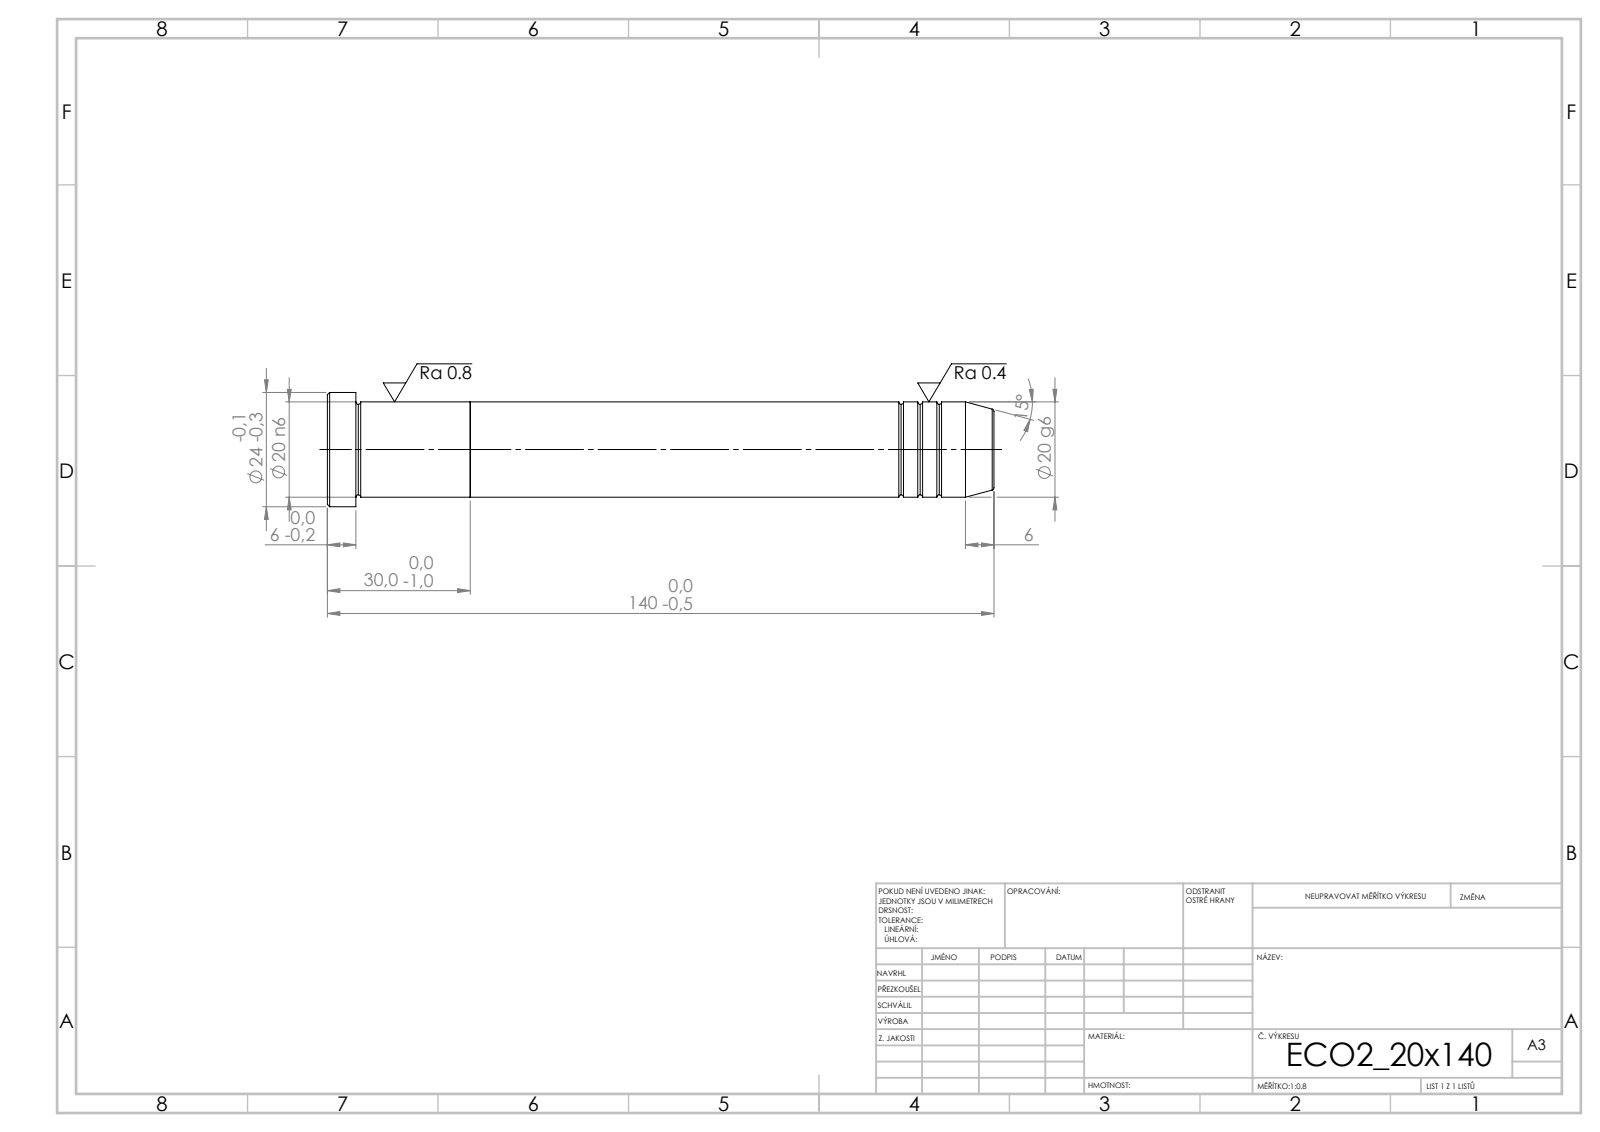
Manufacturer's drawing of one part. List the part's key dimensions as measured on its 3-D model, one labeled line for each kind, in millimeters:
STEP written by: SolidWorks 2019 (CONFIG_CONTROL_DESIGN)
Units: millimetres
Bodies: 2 solids, 39 faces (5 planar, 12 cylindrical, 22 other)
Overall size (bounding box): 140 × 24 × 24
Volume: 44 418 mm³ · Surface area: 10 396 mm²
Round bosses / shafts (diameter × count): ⌀24 ×1, ⌀20 ×1
Main face-to-face distances: 30, 110, 140, 134, 24, 6
